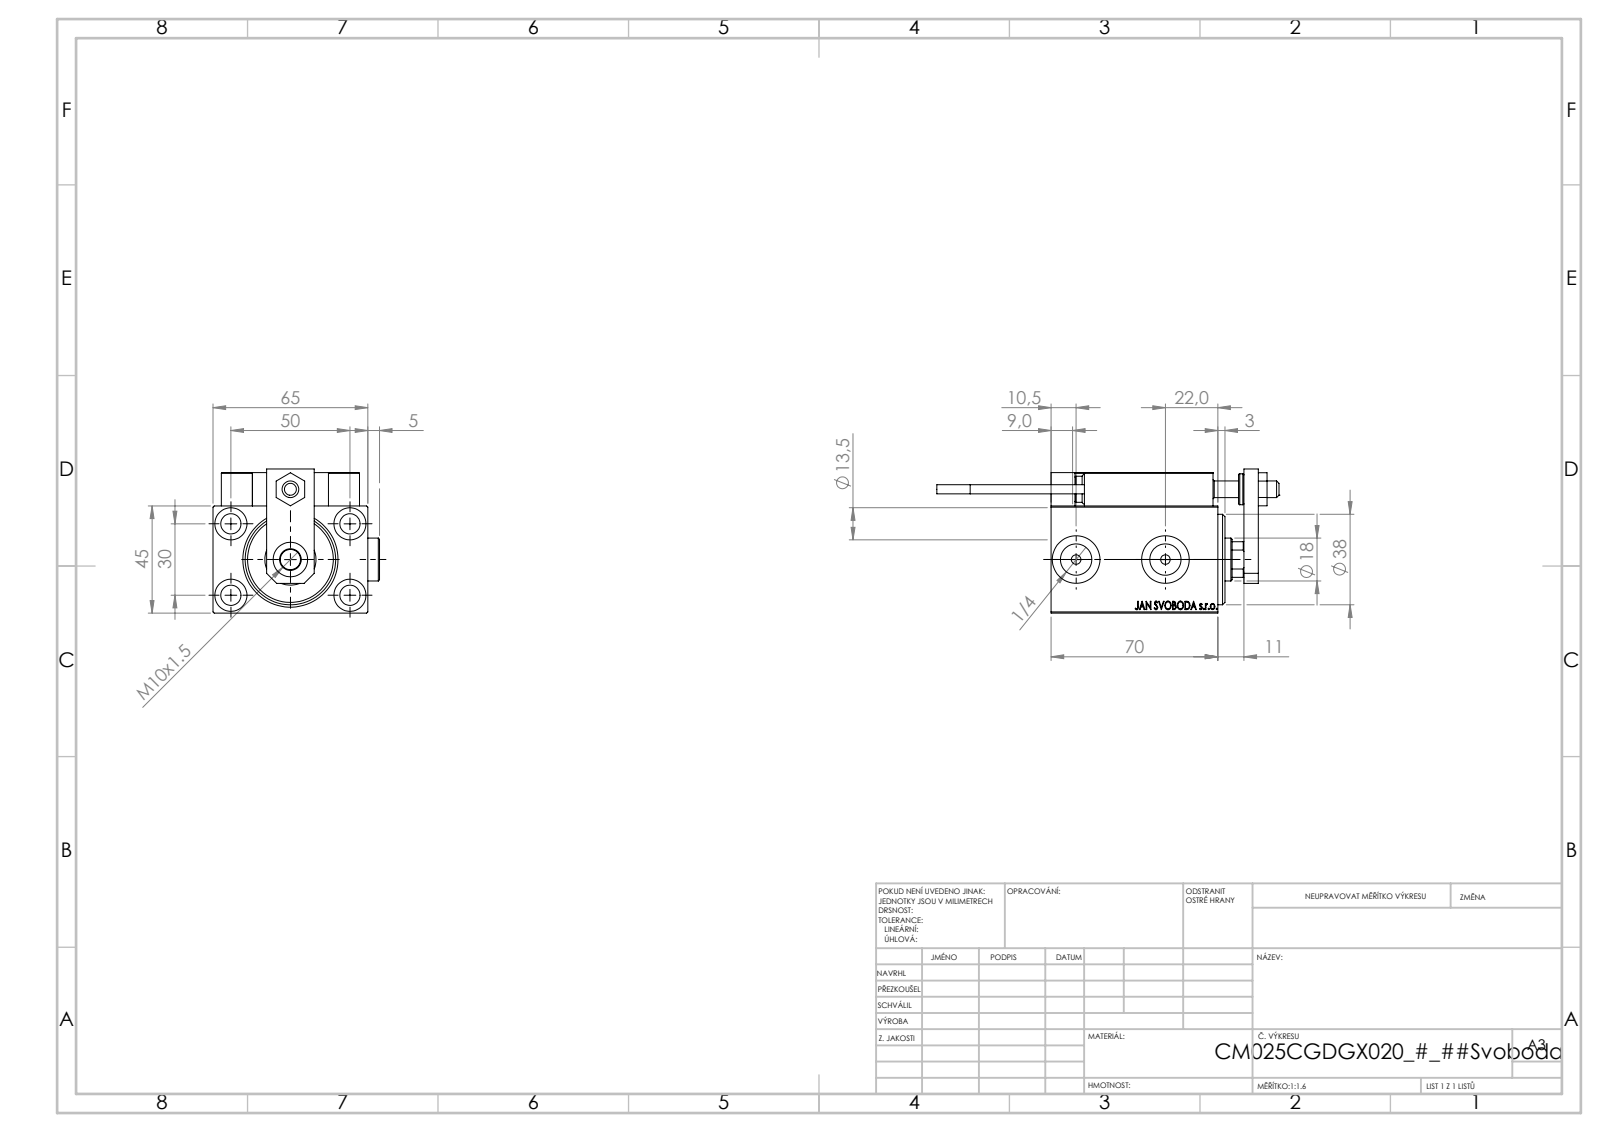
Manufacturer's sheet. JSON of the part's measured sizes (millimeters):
{"part_name": "SWITCH_X_FRONT_BACK; Zatka_OIL_PORT; ALLEN BOLT D5; V450CM_C_Body (+7 more)", "step_written_by": "SolidWorks 2019 (CONFIG_CONTROL_DESIGN)", "units": "millimeters", "bodies": {"solids": 25, "faces": 1336, "planar": 594, "cylindrical": 204, "other": 538}, "overall_size": [143.7, 69.9, 60.5], "volume_mm3": 221635, "surface_area_mm2": 72075, "round_holes": [[4, 6], [8, 5], [8.5, 5], [3.2, 4], [13.5, 4], [5, 2], [13.16, 2], [20, 2], [7, 1], [14.5, 1], [18, 1], [21.5, 1]], "round_bosses_or_shafts": [[18, 2], [5, 2], [3.8, 2], [13, 1], [11, 1]], "partial_cylinders_radius": [[0.3, 30], [3, 2], [8.5, 1]], "face_to_face_distances": [45, 59, 14, 65, 6, 5, 3, 19, 13, 7], "hole_center_spacings": [29.15, 11.37, 20, 22.09, 28.9, 29.59, 29.69, 30]}
